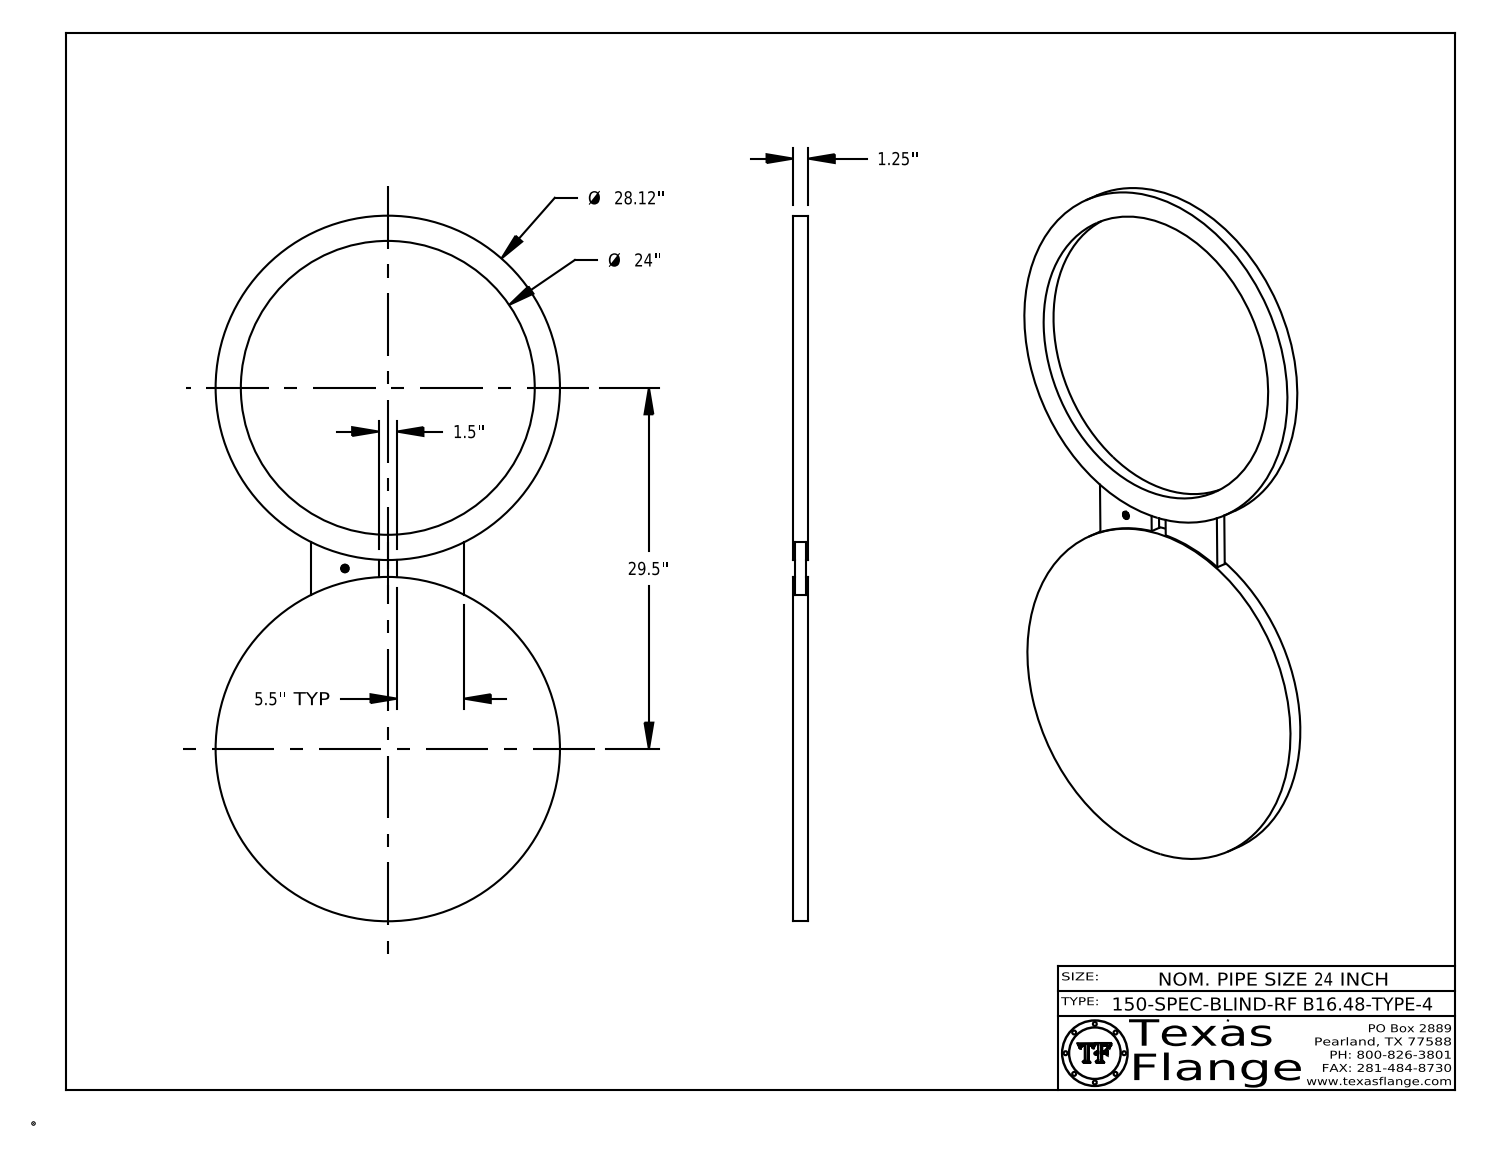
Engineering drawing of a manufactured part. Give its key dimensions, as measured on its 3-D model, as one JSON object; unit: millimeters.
{"part_name": "24-150-SPEC-BLIND-RF-B16.48-TYPE-4", "step_written_by": "CATIA V5 STEP AP214 (AUTOMOTIVE_DESIGN)", "units": "millimeters", "bodies": {"solids": 1, "faces": 403, "planar": 377, "cylindrical": 26, "other": 0}, "overall_size": [1463.5, 714.2, 31.8], "volume_mm3": 16600000, "surface_area_mm2": 1250000, "round_holes": [[15.9, 1], [609.6, 1]], "round_bosses_or_shafts": [[1, 8], [714.2, 2], [12.5, 1]], "face_to_face_distances": [31.8, 4, 27.8, 23.8, 317.5, 139.7, 177.8, 38.1, 27.4, 23.4], "hole_center_spacings": [385]}
